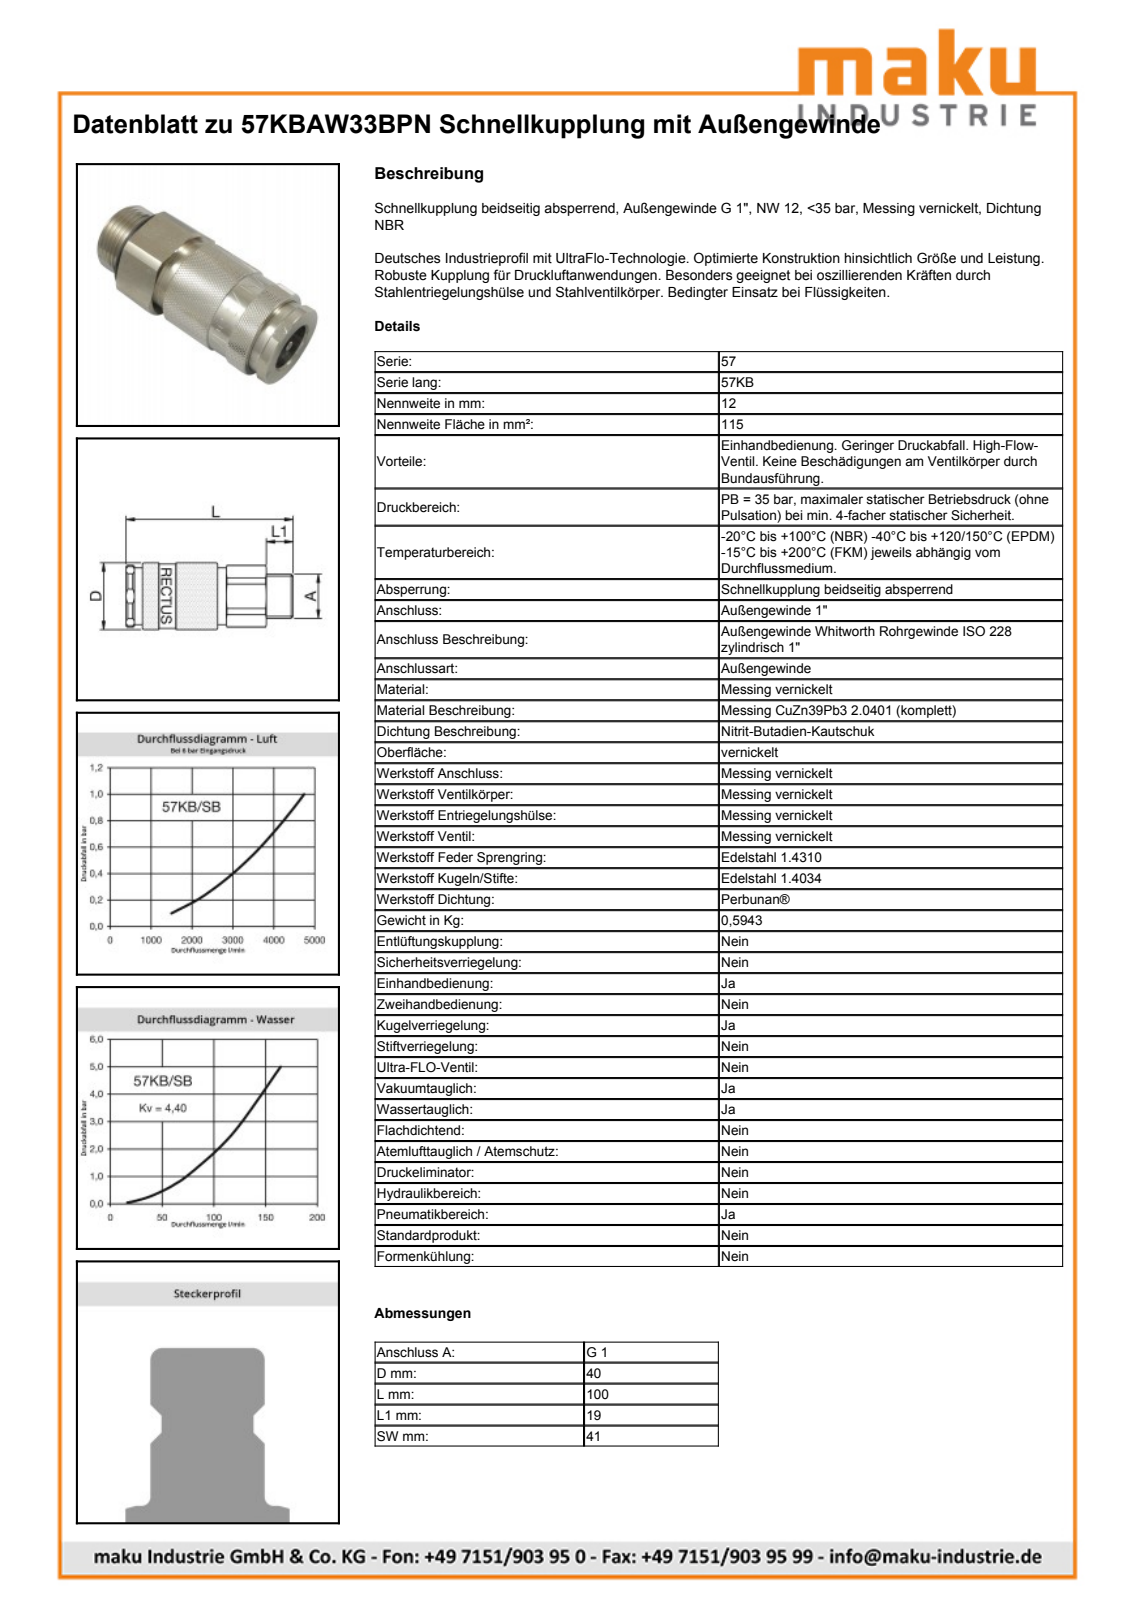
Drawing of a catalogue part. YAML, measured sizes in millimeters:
part_name: "D110179"
step_written_by: "Autodesk Inventor 2013 (AUTOMOTIVE_DESIGN)"
units: millimeters
bodies: {solids: 2, faces: 513, planar: 202, cylindrical: 74, other: 237}
overall_size: [100.05, 44.44, 44.36]
volume: 112944
surface_area: 26939
round_holes:
  - {diameter: 28.95, count: 1}
  - {diameter: 30.2, count: 1}
  - {diameter: 33.4, count: 1}
  - {diameter: 34.2, count: 1}
  - {diameter: 34.6, count: 1}
round_bosses_or_shafts:
  - {diameter: 40, count: 1}
  - {diameter: 38.5, count: 1}
  - {diameter: 34, count: 1}
  - {diameter: 33.25, count: 1}
  - {diameter: 30, count: 1}
  - {diameter: 28.8, count: 1}
  - {diameter: 28.4, count: 1}
  - {diameter: 27.59, count: 1}
partial_cylinders:
  - {radius: 18.5, count: 1}
  - {radius: 19.15, count: 1}
  - {radius: 22.5, count: 1}
face_to_face_distances: [41, 100.05, 60.05, 40, 40.98, 83.05, 23, 17, 37.8, 22.25]
